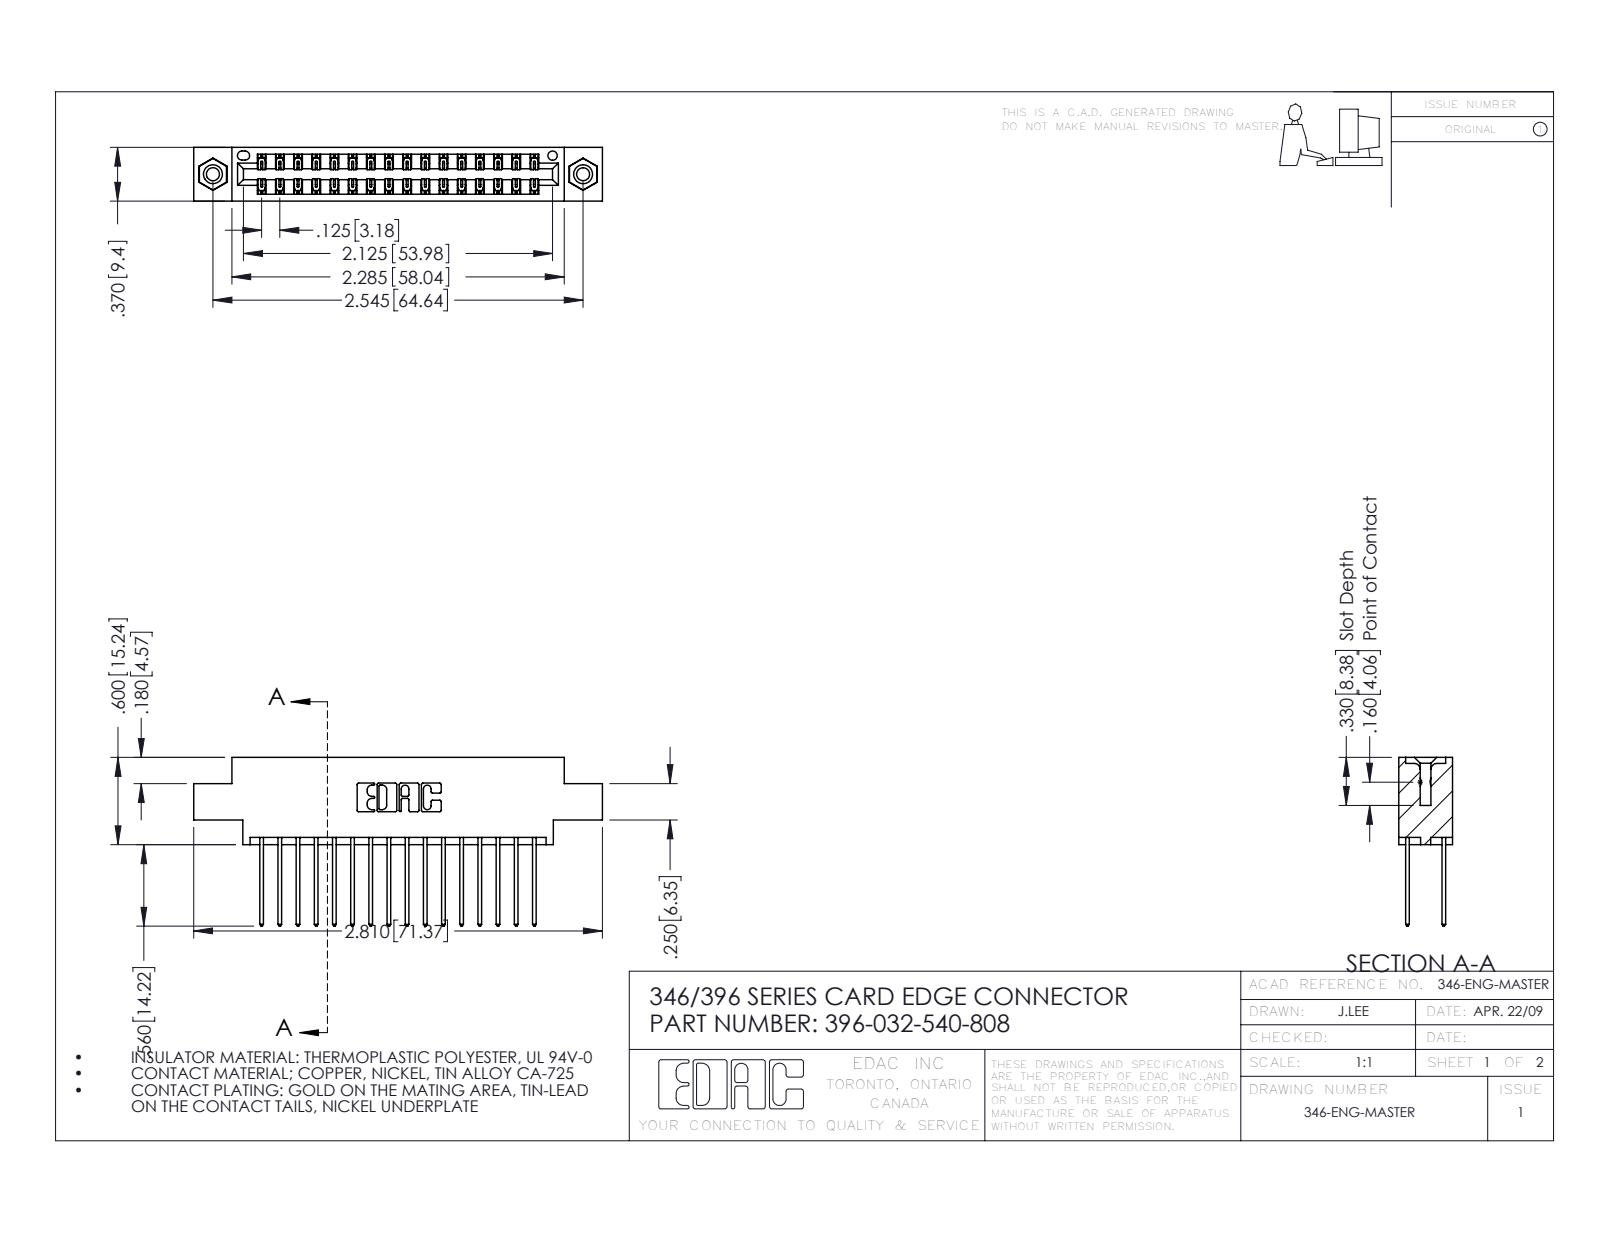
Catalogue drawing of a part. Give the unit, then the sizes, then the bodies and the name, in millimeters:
Units: millimetres
Overall size (bounding box): 71.4 × 29.5 × 9.4
Round holes (diameter × count): ⌀2.3 ×2, ⌀3.2 ×2, ⌀4 ×2, ⌀1.6 ×1
Round bosses / shafts (diameter × count): ⌀3.9 ×2
Partial cylindrical surfaces — rounded edges, fillets, slot ends (radius × count): R0.2 ×48, R0.3 ×32, R0.3 ×22, R0.2 ×6, R0.8 ×6, R0.7 ×3, R0.4 ×2, R0.6 ×2
Main face-to-face distances: 1.2, 8.2, 6.4, 9.4, 1.8, 7.6, 0.6, 7, 5.6, 3.8
Hole centre spacings: 6.2, 59.4, 64.6
Volume: 6 720 mm³ · Surface area: 9 600 mm²
Bodies: 35 solids, 1850 faces (1232 planar, 602 cylindrical, 16 other)
Part name (STEP PRODUCT): 396-032-540-808; 346 Part_0.170 Offset - 0.156 Dia-TI; 345-250-001_345-250-003-102; 345-292-001_345-293-140
STEP written by: SolidWorks 2016 (CONFIG_CONTROL_DESIGN)
